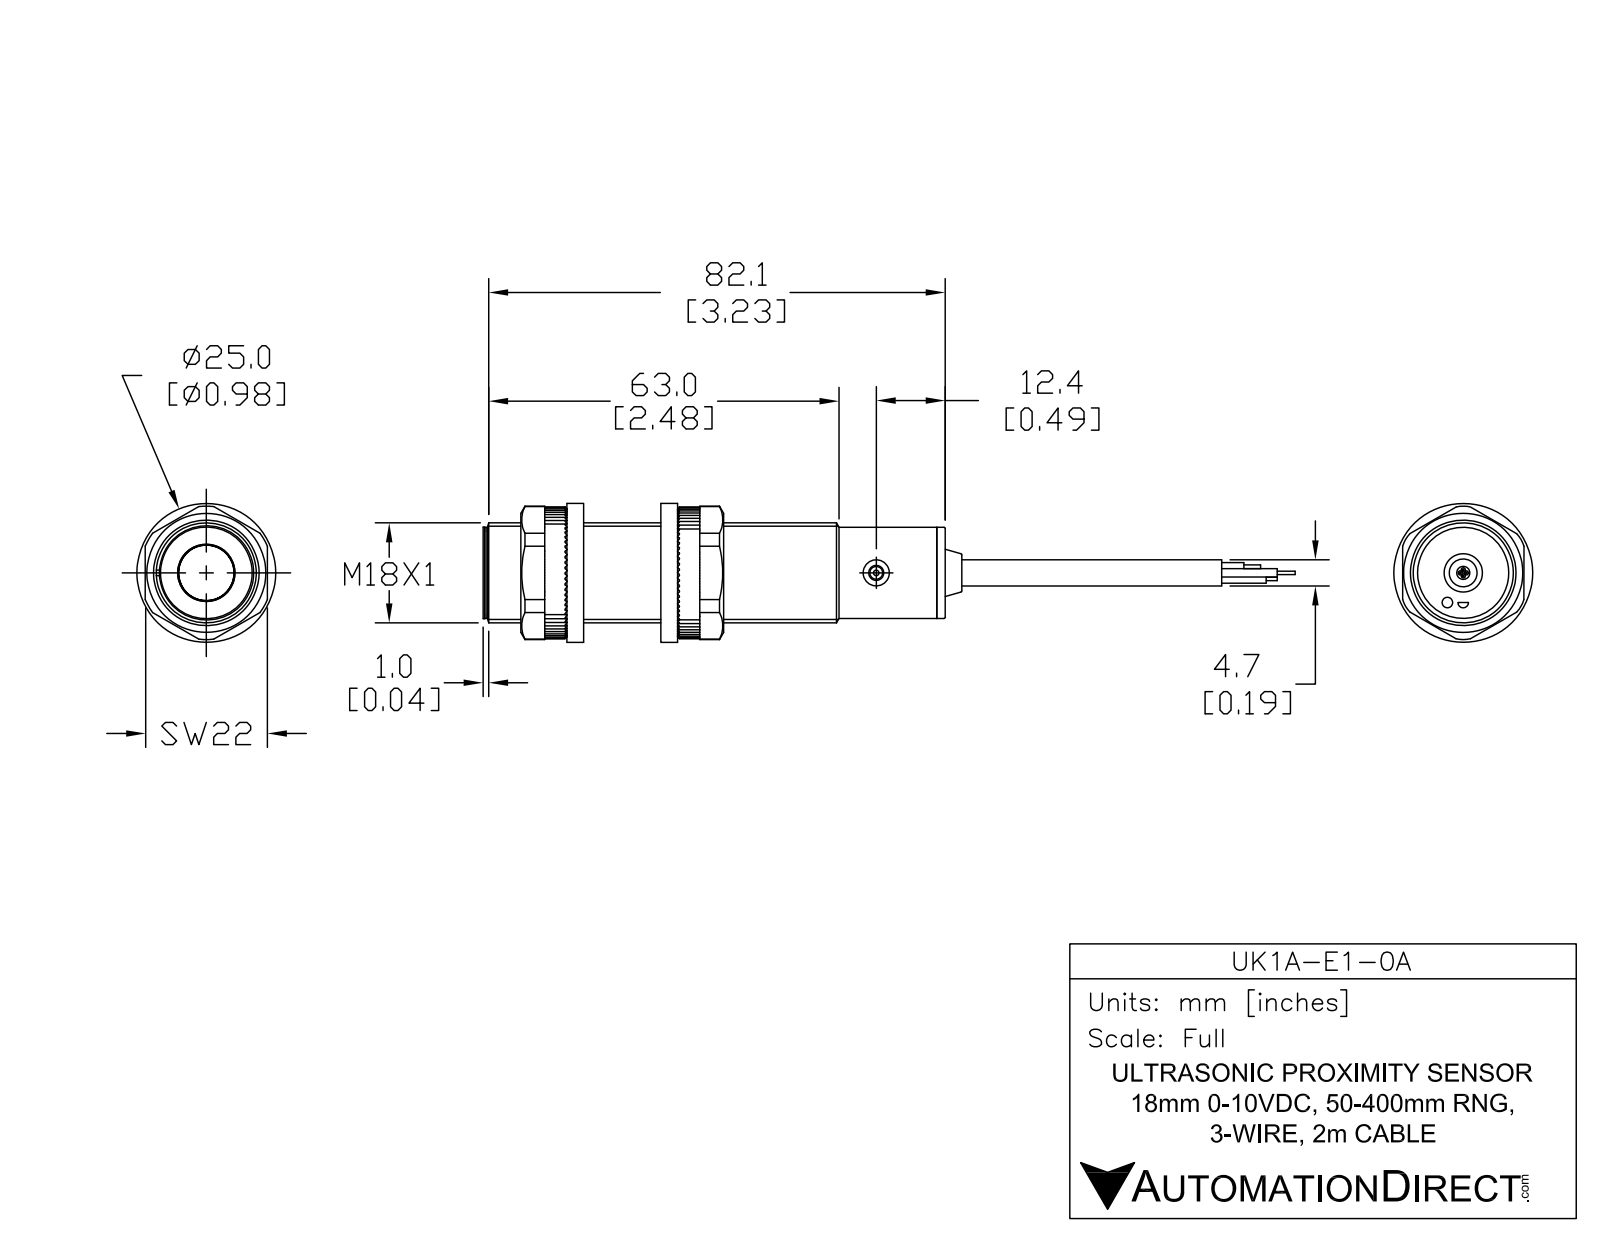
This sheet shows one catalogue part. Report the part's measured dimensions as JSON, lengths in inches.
{"part_name": "UK1A-E1-0A", "step_written_by": "SolidWorks 2017 (AUTOMOTIVE_DESIGN)", "units": "inches", "bodies": {"solids": 6, "faces": 55, "planar": 17, "cylindrical": 24, "other": 14}, "overall_size": [4.832, 0.709, 0.709], "volume_in3": 1.285, "surface_area_in2": 10.69, "round_holes": [[0.185, 2], [0.106, 1]], "round_bosses_or_shafts": [[0.709, 1], [0.646, 1], [0.622, 1], [0.374, 1], [0.189, 1], [0.091, 1]], "face_to_face_distances": [3.193, 3.252, 0.059, 0.039, 3.232, 3.291, 0.041, 3.234, 3.293, 3.257]}
